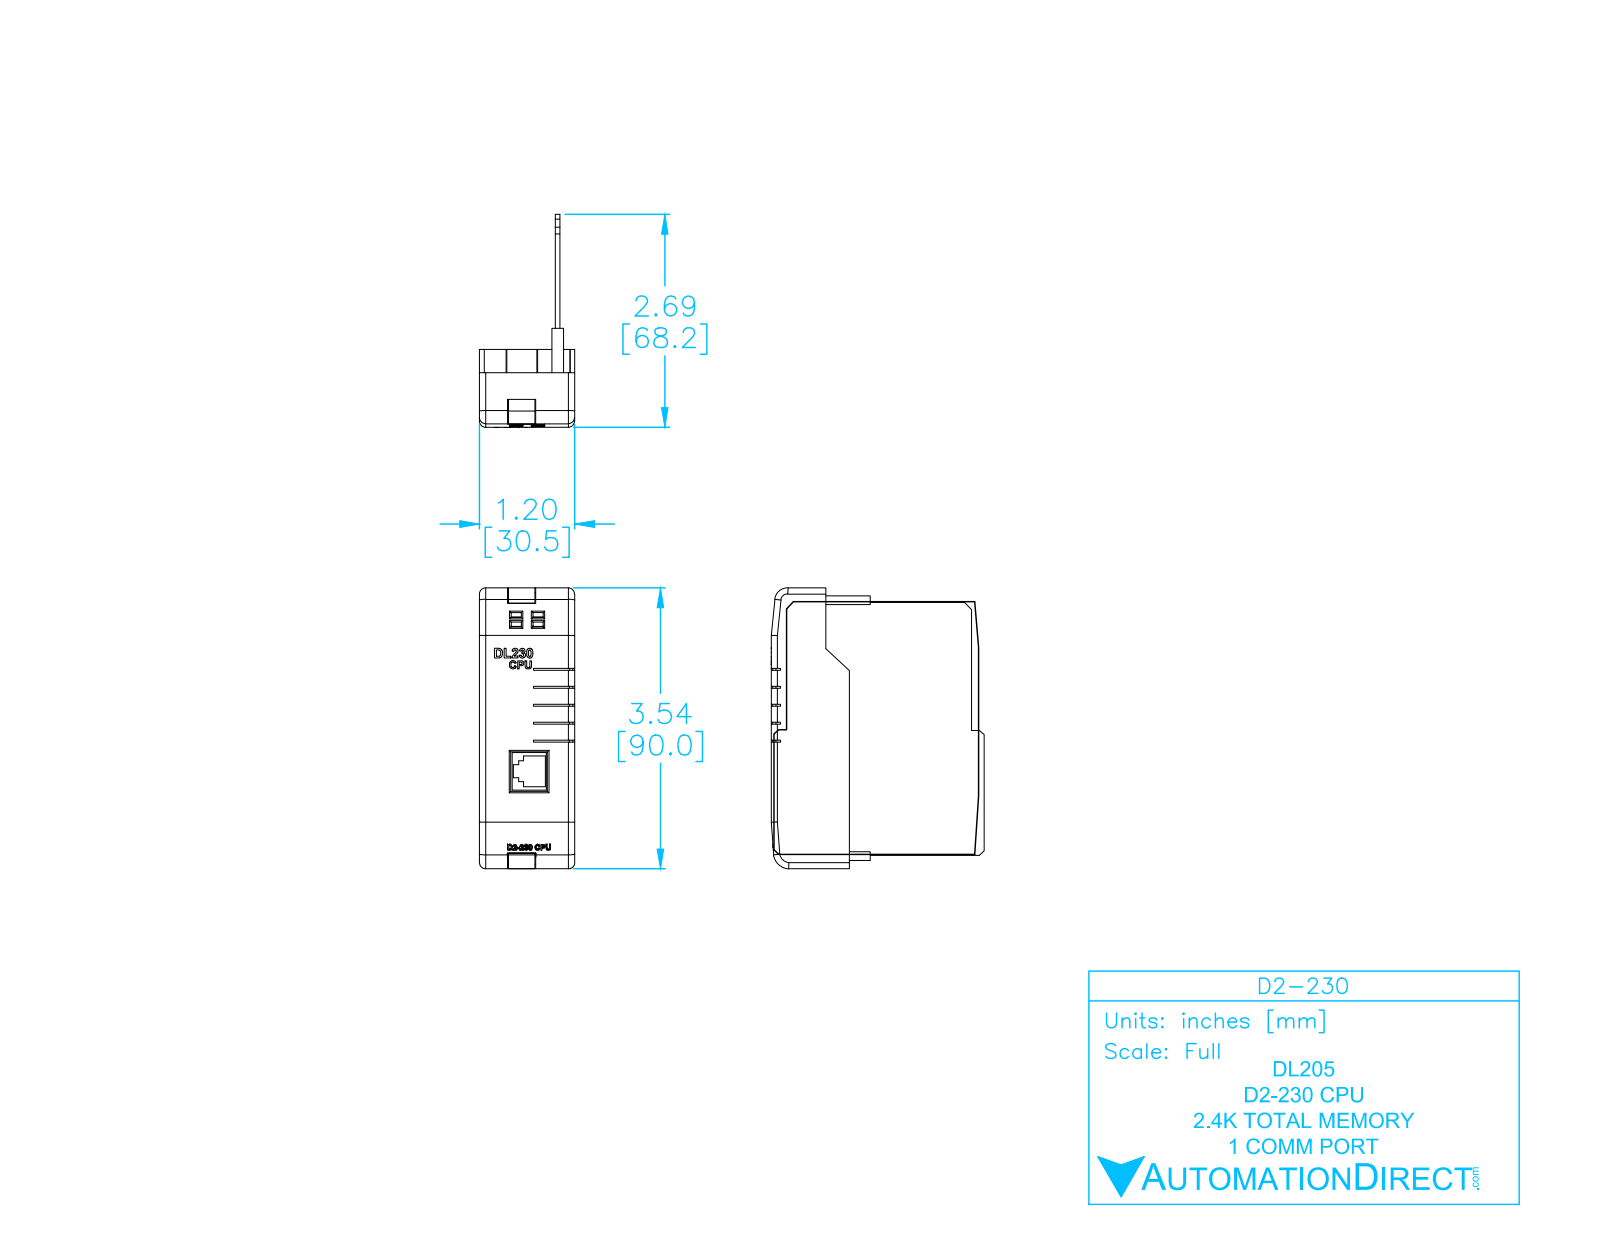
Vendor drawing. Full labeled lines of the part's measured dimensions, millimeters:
Part name (STEP PRODUCT): D2-230
STEP written by: SolidWorks 2009 (AUTOMOTIVE_DESIGN)
Units: millimetres
Bodies: 6 solids, 563 faces (329 planar, 80 cylindrical, 154 other)
Overall size (bounding box): 90 × 68.21 × 30.5
Volume: 20 471 mm³ · Surface area: 30 379 mm²
Partial cylindrical surfaces — rounded edges, fillets, slot ends (radius × count): R0.5 ×25, R2 ×10, R0.25 ×4, R1 ×2, R2.62 ×1, R3.79 ×1, R4.12 ×1, R5.29 ×1
Main face-to-face distances: 1.5, 4.72, 24.28, 29, 3.22, 25.78, 30.5, 6.22, 22.78, 27.5
